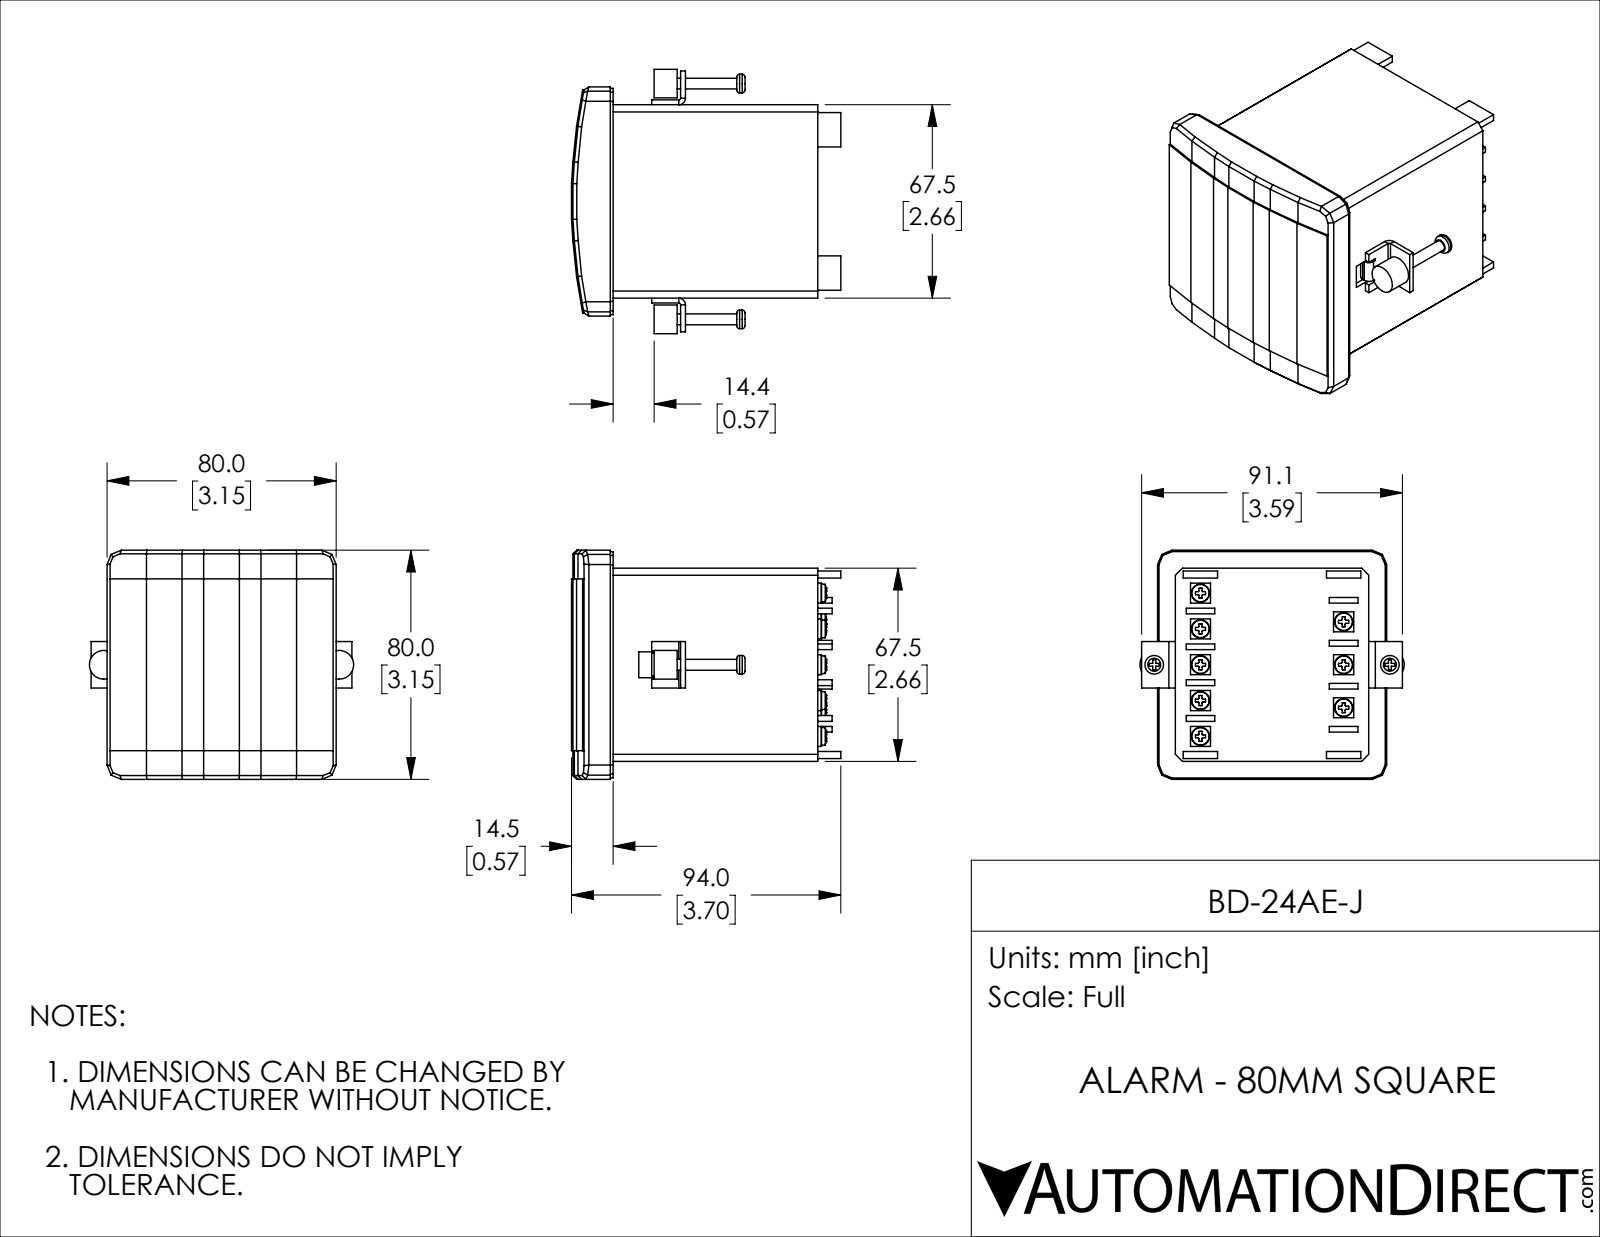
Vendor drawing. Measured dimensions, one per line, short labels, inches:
name: BD-24AE-J
written by: SolidWorks 2018 (AUTOMOTIVE_DESIGN)
unit: in
bodies: 5 solids, 493 faces (366 planar, 88 cylindrical, 39 other)
size: 3.701 × 3.634 × 3.15
volume: 25.1 in³; area: 65.35 in²
holes: 2× ⌀0.152
bosses: 8× ⌀0.248, 2× ⌀0.394, 2× ⌀0.256, 2× ⌀0.15
rounds: 8× R0.038, 8× R0.684, 6× R0.024, 6× R0.091, 1× R1.811
face distances: 2.657, 0.246, 2.904, 2.815, 3.15, 0.02, 0.571, 0.197, 3.386, 0.039
hole spacings: 3.24
